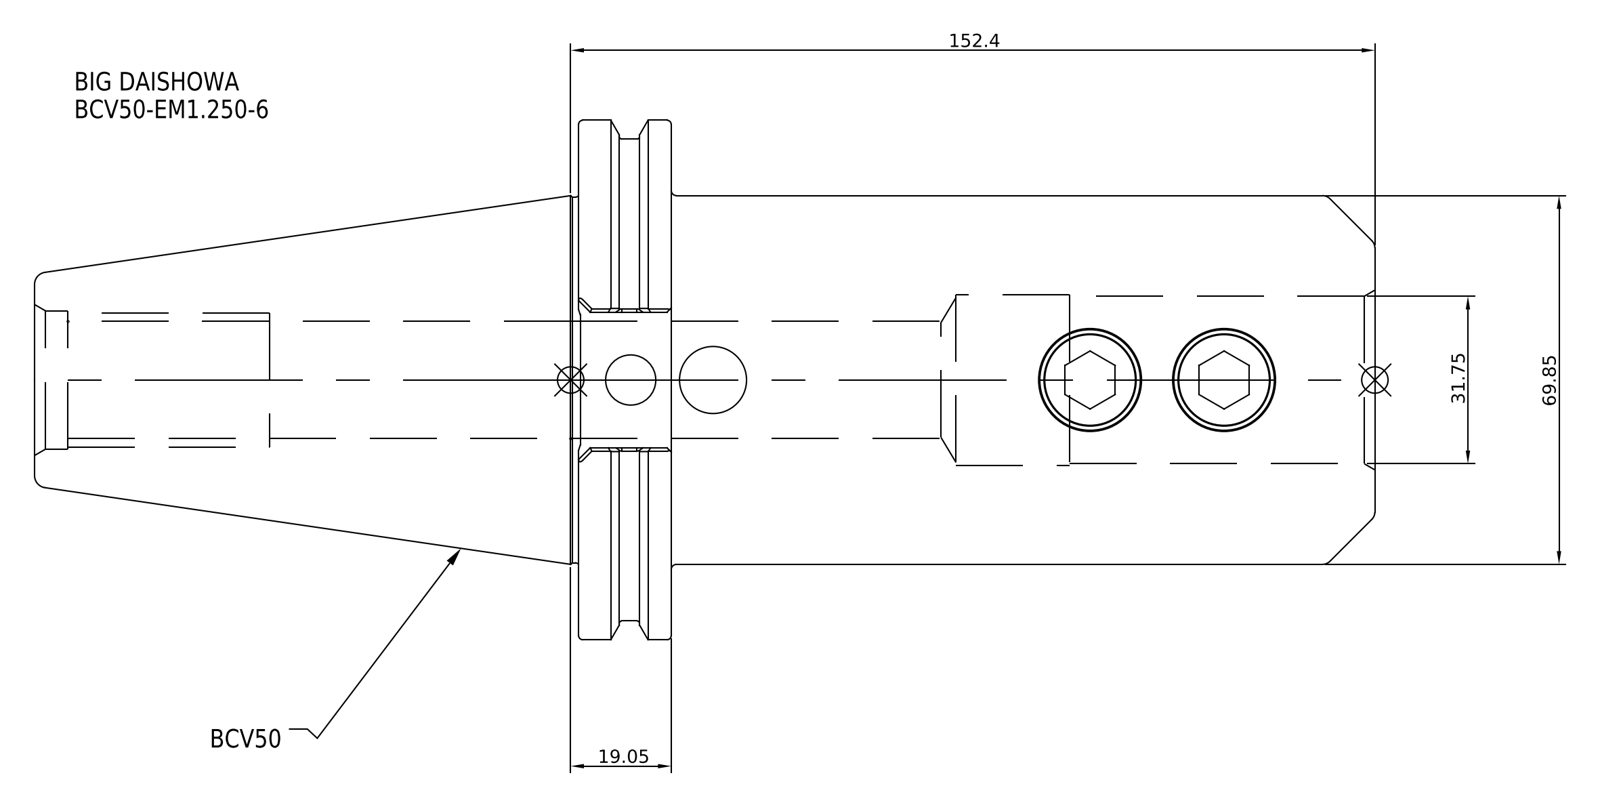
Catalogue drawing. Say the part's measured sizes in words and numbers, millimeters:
The part is named "BCV50-EM1_250-6". Its 3-D file was written by "SolidWorks 2021 (CONFIG_CONTROL_DESIGN)". It is 1 solid with 27 faces: 7 planar, 12 cylindrical and 8 other. Overall it measures 254 by 98.43 by 98.43 millimeters. Its volume is 791 148 cubic millimeters and its surface area 77 163 square millimeters. Round holes: 1 of diameter 31.75. Round bosses or shafts: 1 of diameter 98.43, 1 of diameter 91.29, 1 of diameter 69.85. The main face-to-face distances are 17.55, 133.35, 150.9, 254, 120.65, 103.1, 117.35, 16, 33.55, 136.65.
